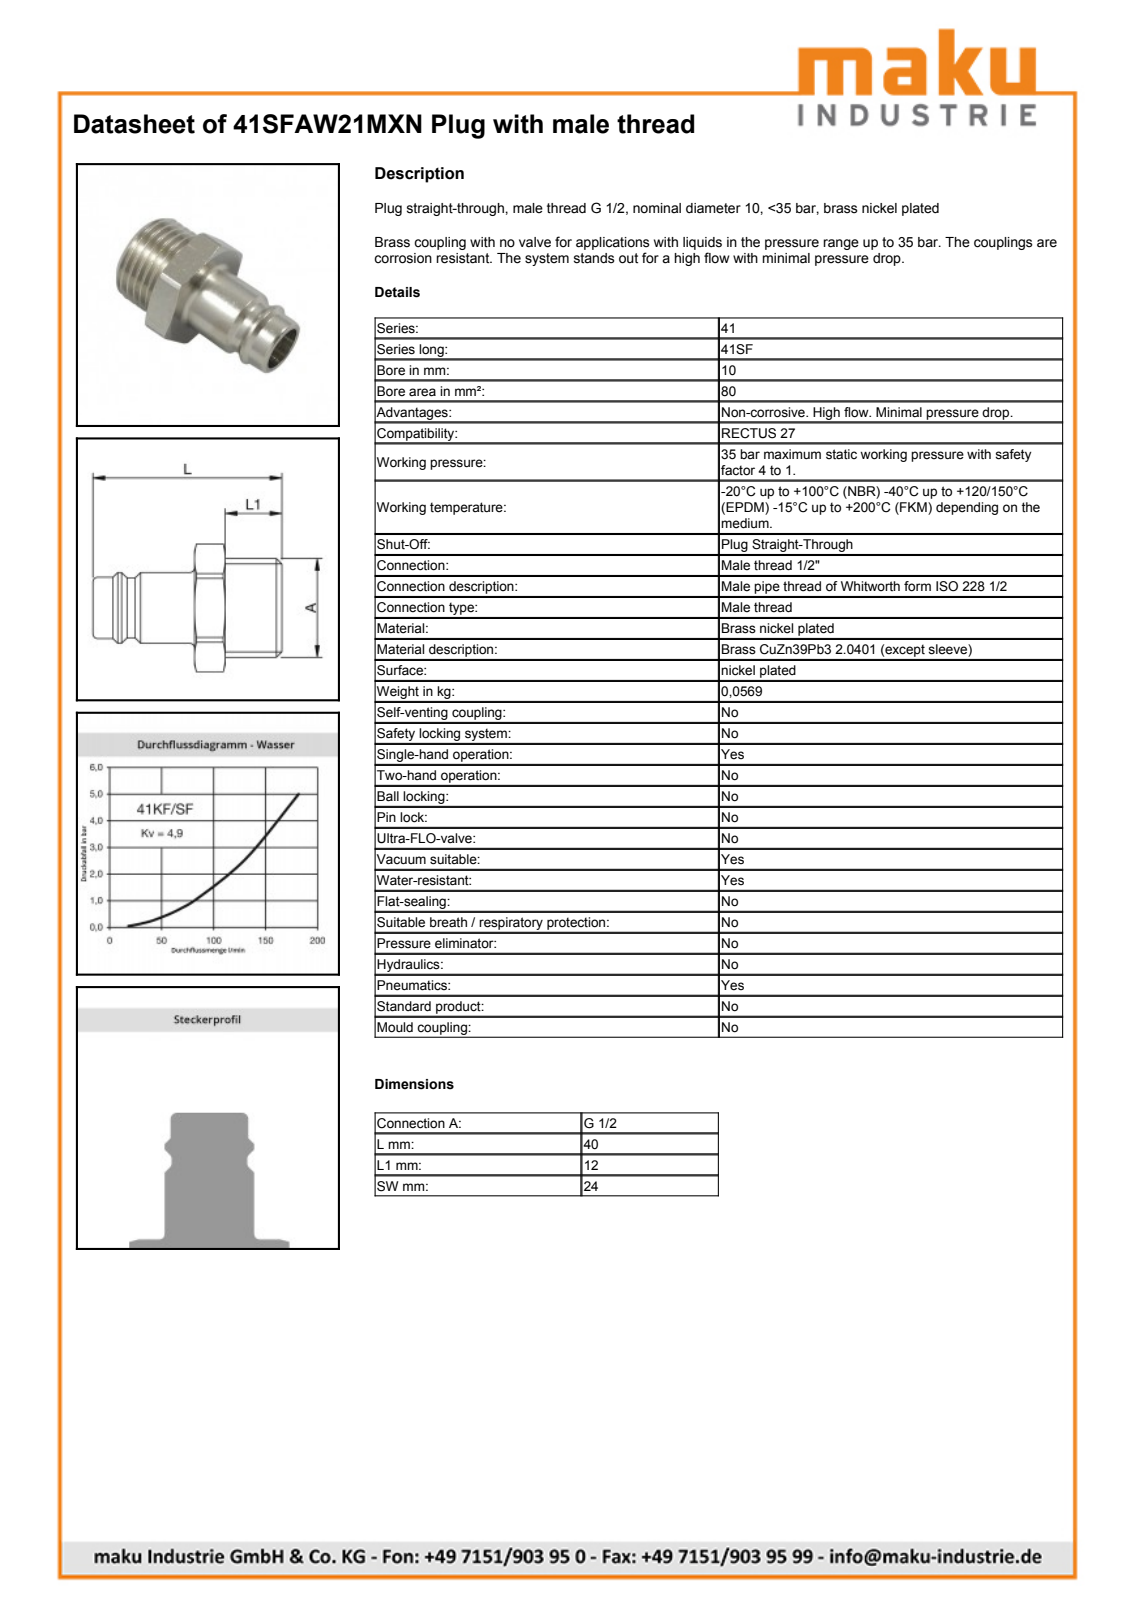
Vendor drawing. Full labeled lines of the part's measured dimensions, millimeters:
Part name (STEP PRODUCT): D108298
STEP written by: Autodesk Inventor 2013 (AUTOMOTIVE_DESIGN)
Units: millimetres
Bodies: 1 solid, 43 faces (10 planar, 12 cylindrical, 21 other)
Overall size (bounding box): 40 × 27.05 × 24
Volume: 7 270 mm³ · Surface area: 4 256 mm²
Round holes (diameter × count): ⌀10 ×1
Round bosses / shafts (diameter × count): ⌀20.96 ×1, ⌀15 ×1, ⌀13 ×1, ⌀12.6 ×1
Partial cylindrical surfaces — rounded edges, fillets, slot ends (radius × count): R13.53 ×1
Main face-to-face distances: 24, 6.5, 18.5, 12, 21.5, 28, 40
